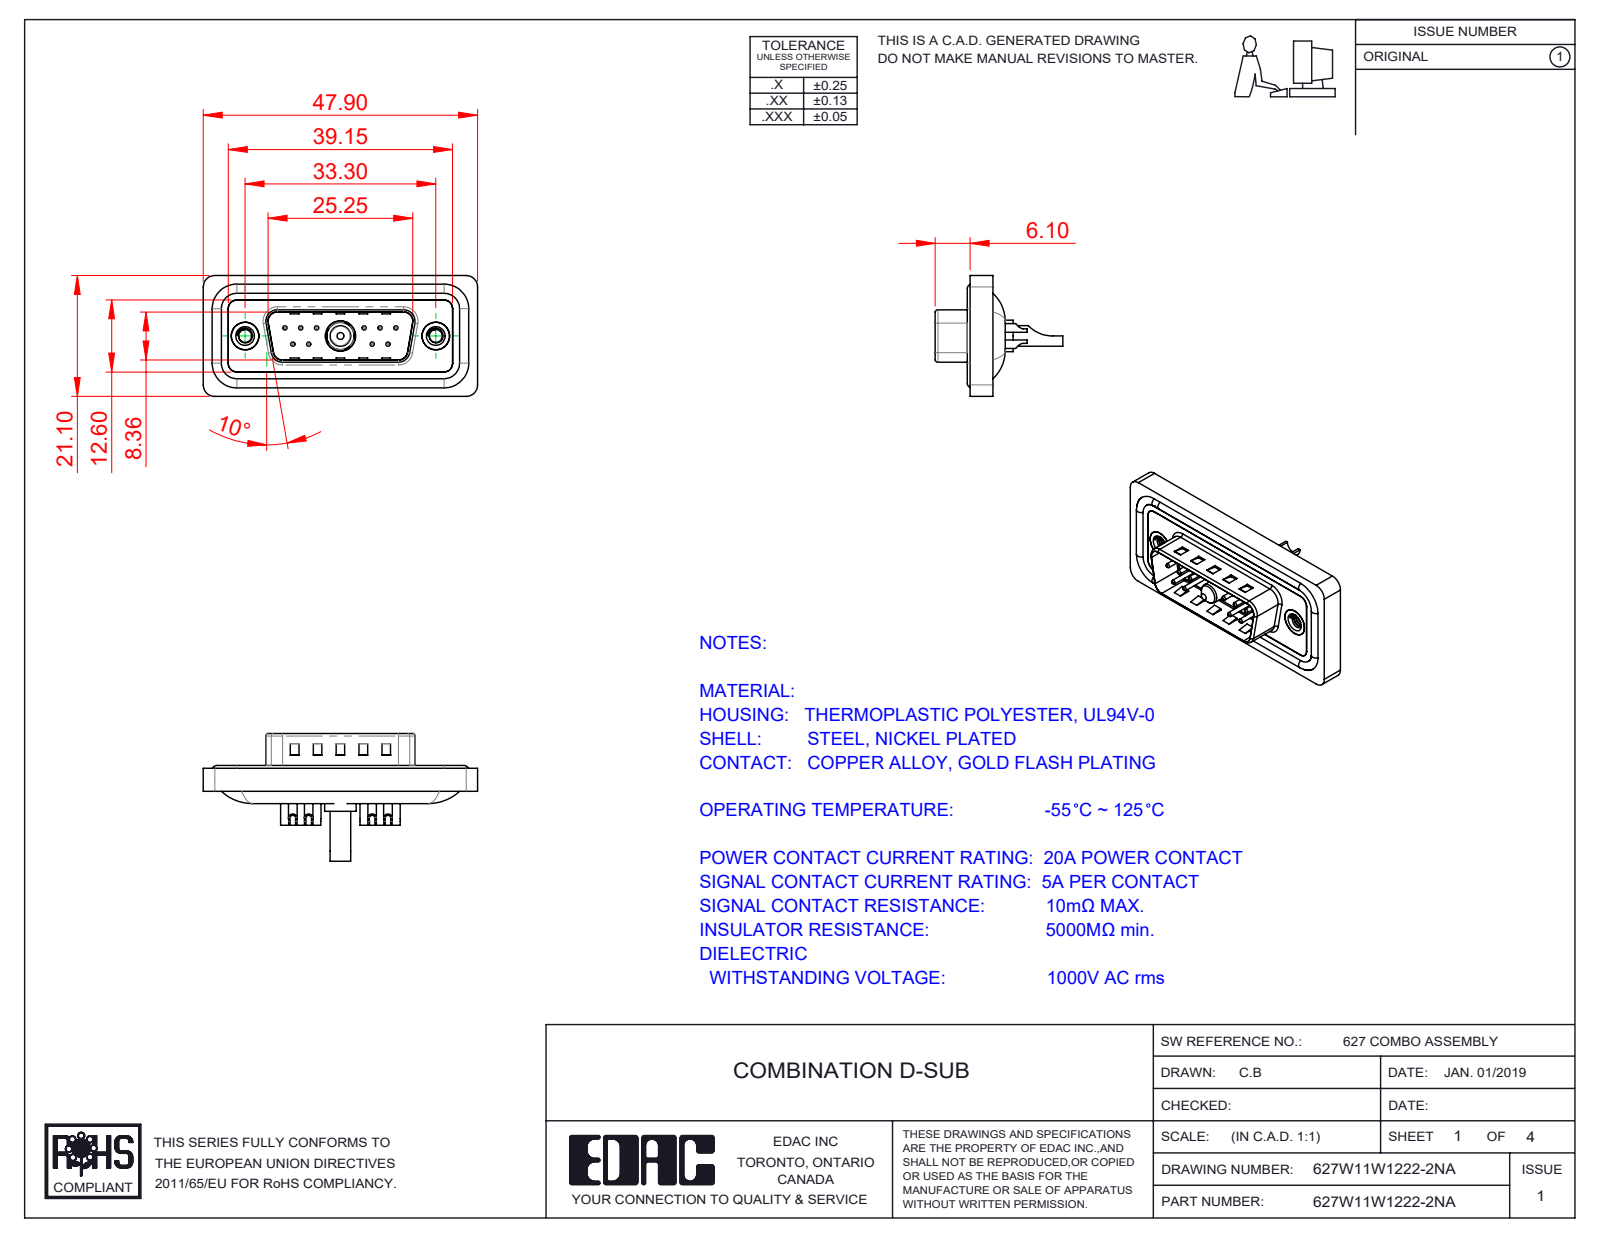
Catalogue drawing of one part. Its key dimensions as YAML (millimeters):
part_name: "627W11W1222-2NA; 627Combo Contact Row 2_22; Power Pin_20A SC; 627Combo Shell Front_15 Contacts (+5 more)"
step_written_by: "SolidWorks 2020 (CONFIG_CONTROL_DESIGN)"
units: millimeters
bodies: {solids: 19, faces: 873, planar: 289, cylindrical: 372, other: 212}
overall_size: [47.9, 22.3, 21.1]
volume: 5478
surface_area: 8996
round_holes:
  - {diameter: 0.75, count: 10}
  - {diameter: 1, count: 10}
  - {diameter: 1.6, count: 10}
  - {diameter: 2, count: 10}
  - {diameter: 2.26, count: 2}
  - {diameter: 4, count: 2}
  - {diameter: 4.8, count: 2}
  - {diameter: 5, count: 2}
  - {diameter: 2.7, count: 1}
  - {diameter: 4.85, count: 1}
  - {diameter: 5.3, count: 1}
round_bosses_or_shafts:
  - {diameter: 1.5, count: 10}
  - {diameter: 1.6, count: 4}
  - {diameter: 4.9, count: 2}
  - {diameter: 5.5, count: 1}
  - {diameter: 5.2, count: 1}
  - {diameter: 4.75, count: 1}
  - {diameter: 3.75, count: 1}
  - {diameter: 3.6, count: 1}
partial_cylinders:
  - {radius: 1.5, count: 26}
  - {radius: 2, count: 20}
  - {radius: 1, count: 9}
  - {radius: 0.5, count: 8}
  - {radius: 1.6, count: 8}
  - {radius: 0.25, count: 4}
  - {radius: 0.6, count: 4}
  - {radius: 0.65, count: 4}
face_to_face_distances: [0.4, 1.1, 1.6, 1.5, 0.5, 2.9, 3.1, 2.5, 4.1, 0.82]
hole_center_spacings: [3.16, 2.77, 13.85, 11.08, 16.62, 5.03, 5.04, 5.54]
